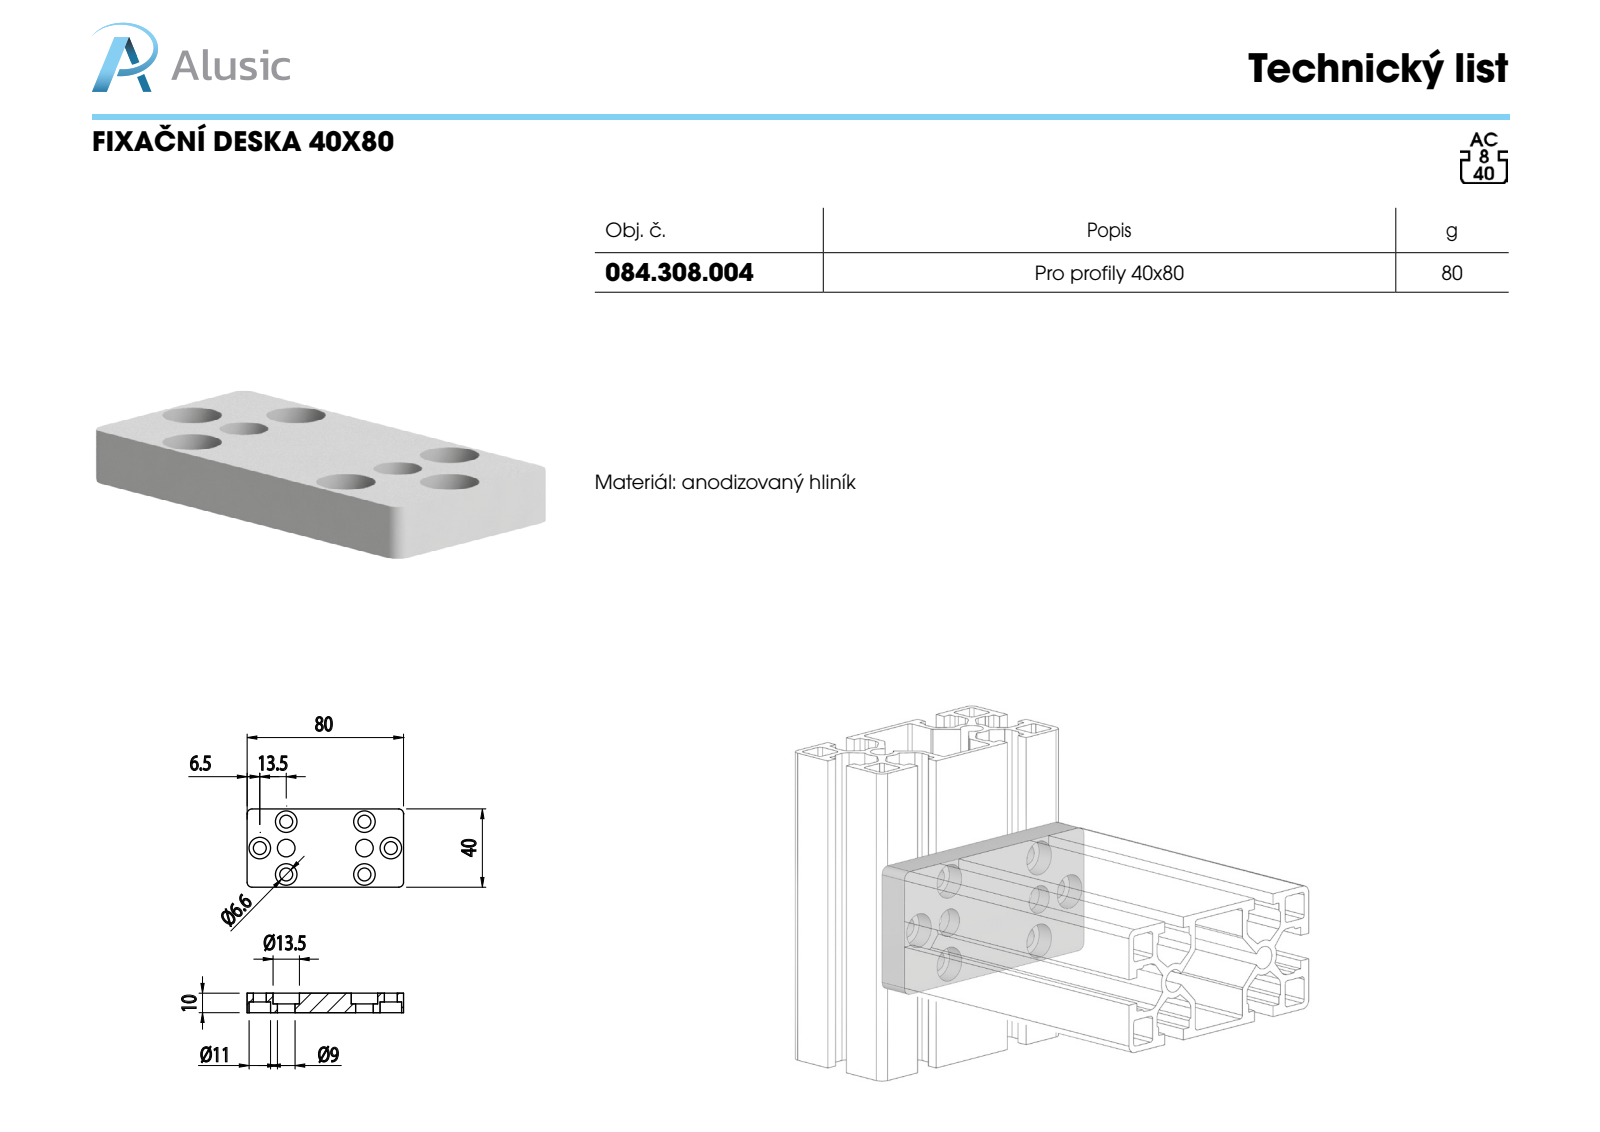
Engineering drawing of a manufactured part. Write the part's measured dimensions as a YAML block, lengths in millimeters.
part_name: "084.308.004"
step_written_by: "SolidWorks 2011 (CONFIG_CONTROL_DESIGN)"
units: millimeters
bodies: {solids: 1, faces: 50, planar: 14, cylindrical: 36, other: 0}
overall_size: [80, 40, 10]
volume: 25739
surface_area: 10503
round_holes:
  - {diameter: 6.6, count: 6}
  - {diameter: 11, count: 6}
  - {diameter: 9, count: 2}
  - {diameter: 13.5, count: 2}
partial_cylinders:
  - {radius: 2.5, count: 4}
face_to_face_distances: [10, 40, 4.5, 5.5, 80, 1]
hole_center_spacings: [13.5, 19.09, 42.22, 55.18, 40, 27, 48.26, 53.5]
